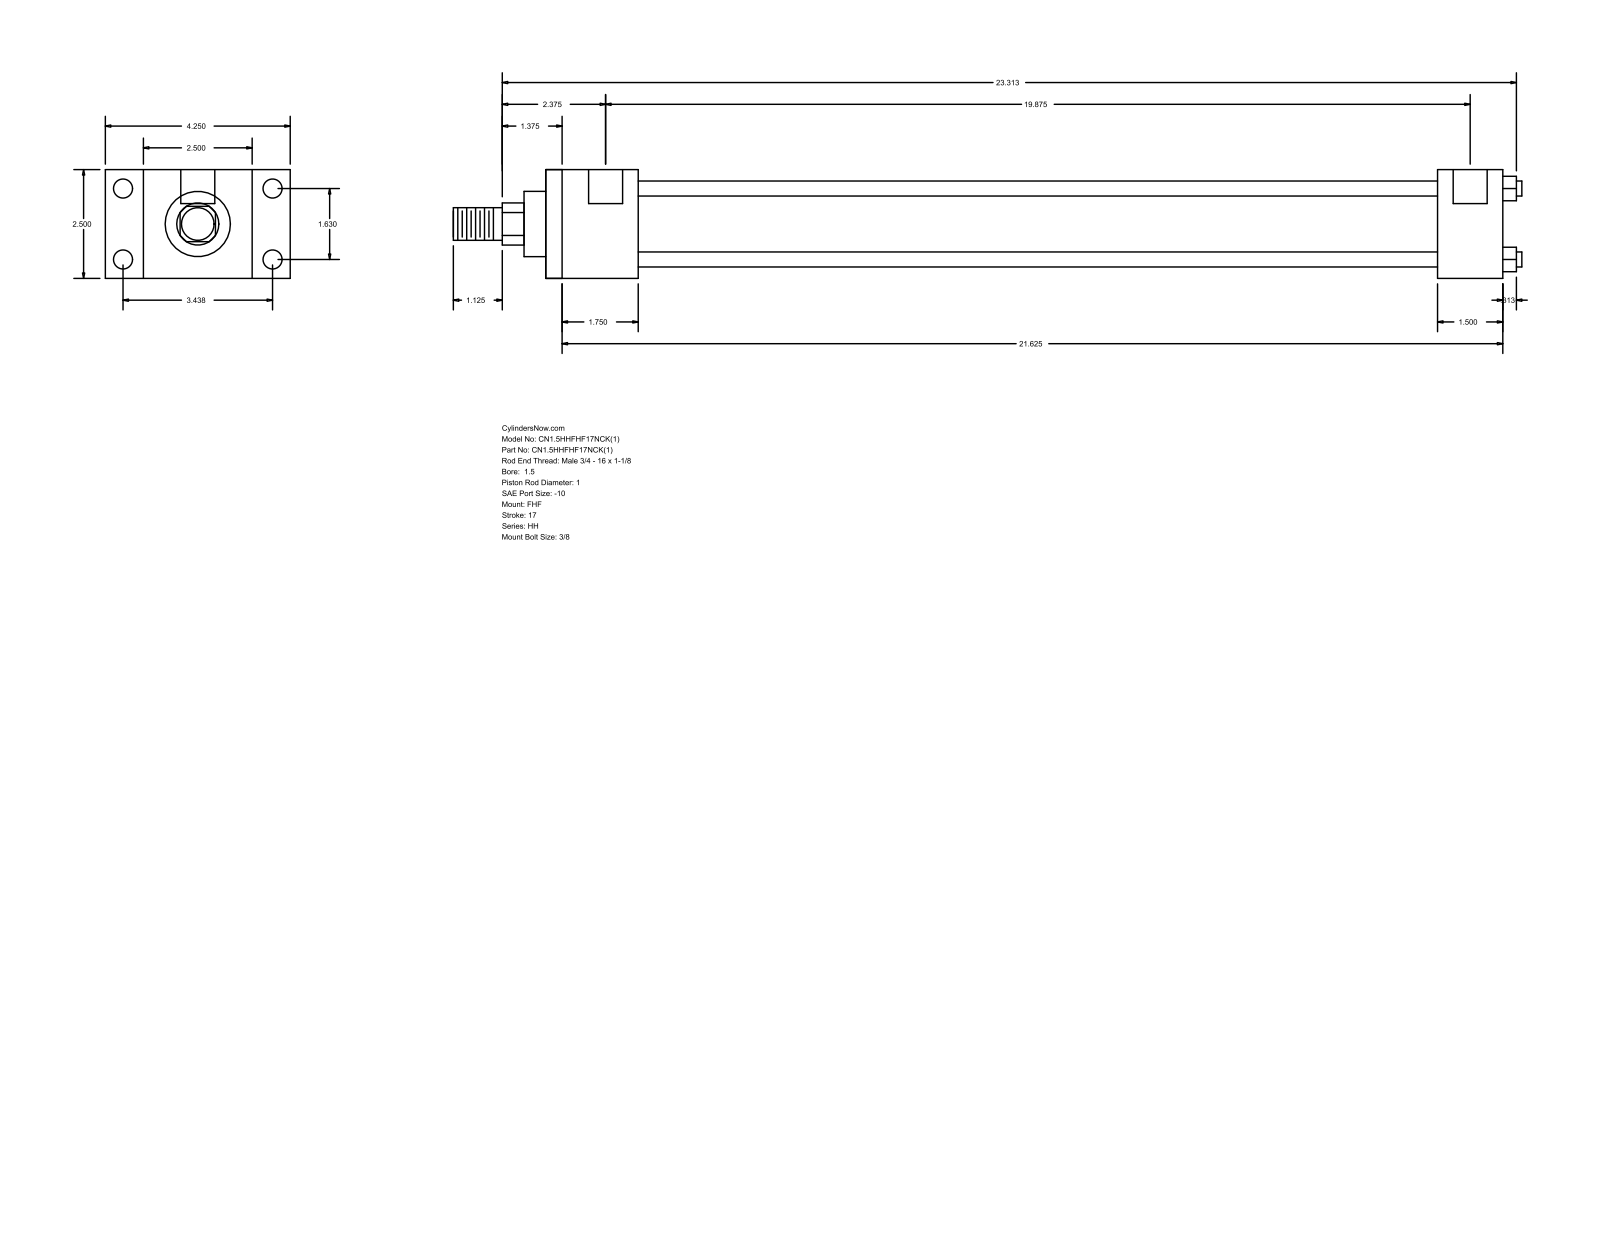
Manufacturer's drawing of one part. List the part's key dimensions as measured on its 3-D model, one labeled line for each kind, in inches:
Part name (STEP PRODUCT): HH_FHF__0150_1
STEP written by: GSSL Pune (CONFIG_CONTROL_DESIGN)
Units: inches
Bodies: 0 solids, 88 faces (60 planar, 28 cylindrical, 0 other)
Overall size (bounding box): 24.563 × 4.25 × 2.5
Round holes (diameter × count): ⌀0.219 ×4, ⌀0.438 ×4, ⌀0.781 ×2
Round bosses / shafts (diameter × count): ⌀0.345 ×4, ⌀1.75 ×1, ⌀1.5 ×1, ⌀1 ×1, ⌀0.75 ×1
Partial cylindrical surfaces — rounded edges, fillets, slot ends (radius × count): R0.484 ×1
Main face-to-face distances: 2.5, 0.875, 3.375, 2.125, 4.25, 22, 19.875, 1.5, 20.5, 18.375
Hole centre spacings: 0.063, 1.63, 3.438, 3.805, 19.937, 20, 19.875
